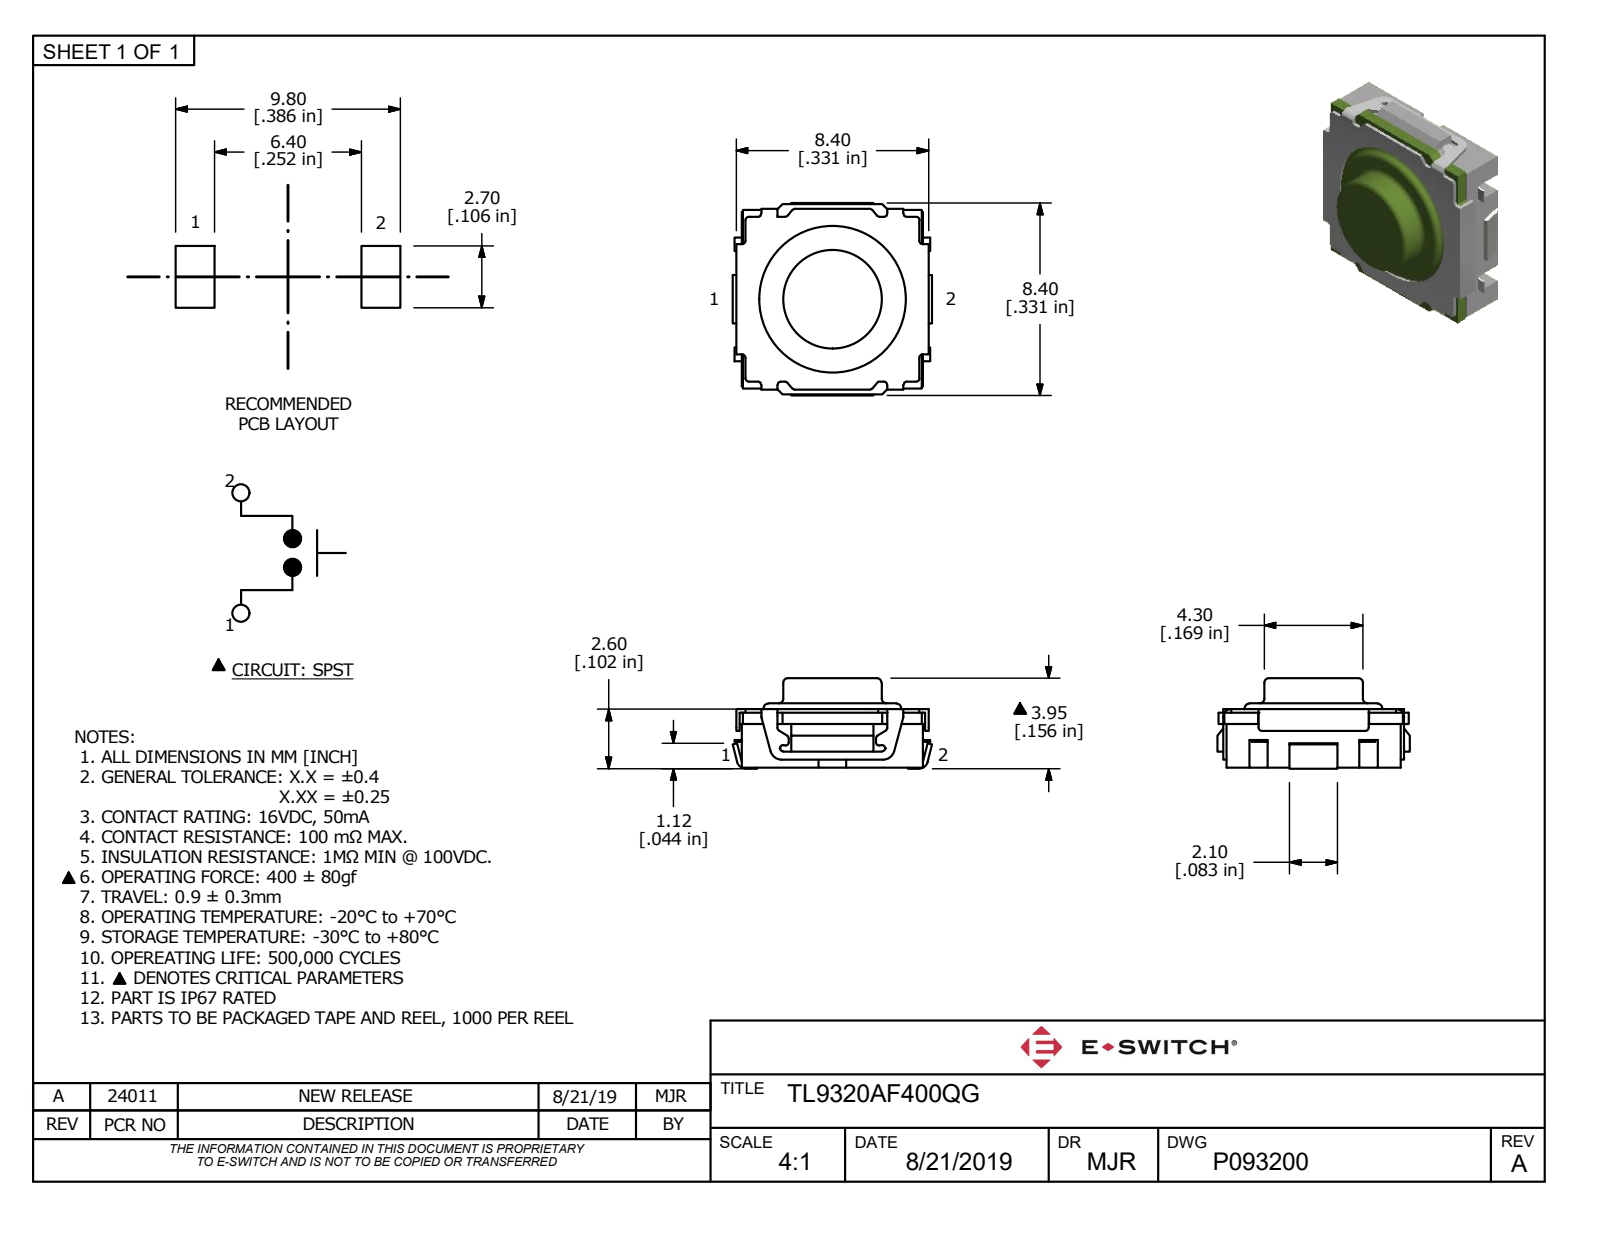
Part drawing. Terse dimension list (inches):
name: TL9320AF400QG
written by: Autodesk Inventor 2018 (AP242_MANAGED_MODEL_BASED_3D_ENGINEERING_MIM_LF)
unit: in
bodies: 1 solid, 290 faces (213 planar, 66 cylindrical, 11 other)
size: 0.343 × 0.331 × 0.156
volume: 0.008 in³; area: 0.594 in²
holes: 1× ⌀0.181, 1× ⌀0.252
bosses: 1× ⌀0.169
rounds: 26× R0.006, 8× R0.006, 4× R0.039, 2× R0.012, 2× R0.016, 2× R0.02
face distances: 0.053, 0.047, 0.1, 0.055, 0.045, 0.028, 0.03, 0.026, 0.075, 0.016
